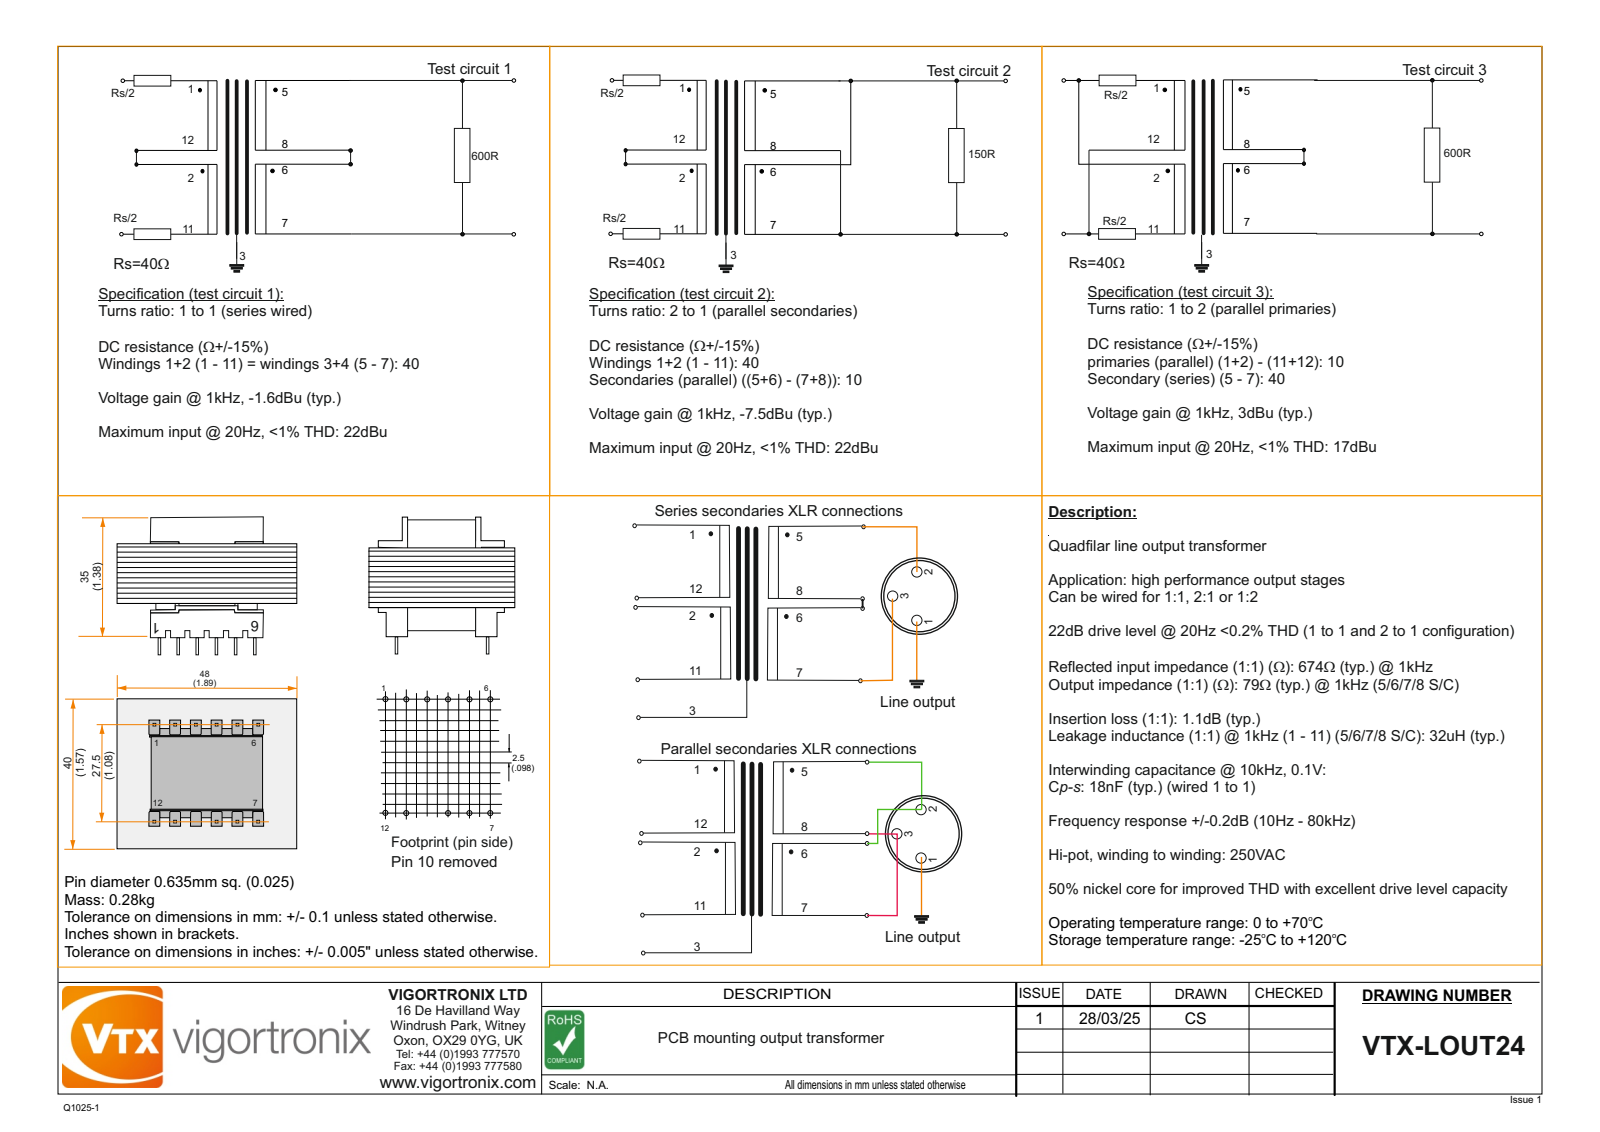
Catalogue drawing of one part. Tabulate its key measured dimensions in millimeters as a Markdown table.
| quantity | value |
| --- | --- |
| part name | I48; Line Output Bobbin EI48; EI48 X 16.8 Winding; E48 (+2 more) |
| STEP written by | SolidWorks 2024 (AUTOMOTIVE_DESIGN) |
| units | millimeters |
| bodies | 97 solids, 1237 faces (1144 planar, 91 cylindrical, 2 other) |
| overall size | 48 × 40.01 × 39.5 |
| volume | 44 705 mm³ |
| surface area | 149 060 mm² |
| partial cylindrical surfaces (radius × count) | 0.5 × 53, 7 × 4, 2 × 2 |
| main face-to-face distances | 0.8, 1.6, 2.4, 3.2, 4, 4.8, 5.6, 8, 6.4, 7.2 |
